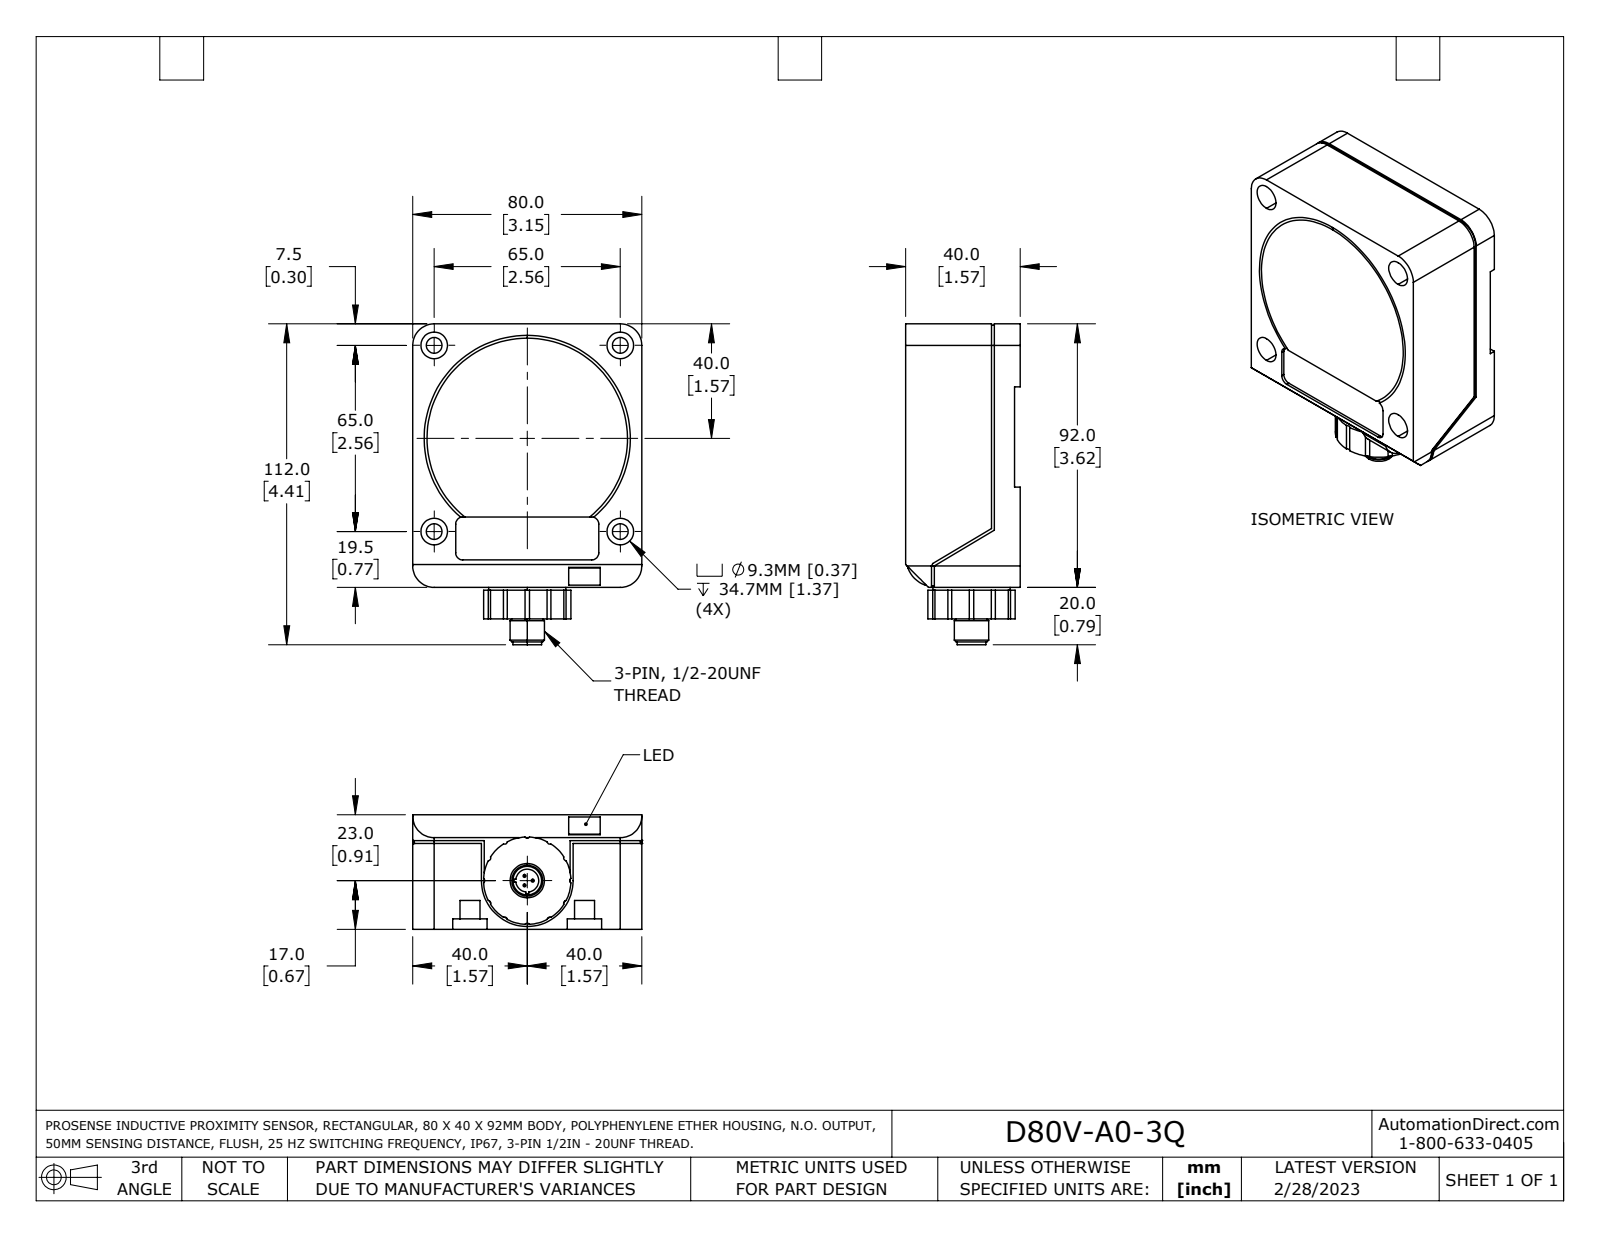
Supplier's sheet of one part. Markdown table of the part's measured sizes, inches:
| quantity | value |
| --- | --- |
| part name | D80V-A0-3M |
| STEP written by | SolidWorks 2021 (AUTOMOTIVE_DESIGN) |
| units | inches |
| bodies | 1 solid, 164 faces (85 planar, 70 cylindrical, 9 other) |
| overall size | 4.409 × 3.15 × 1.575 |
| volume | 17.35 in³ |
| surface area | 52.6 in² |
| round holes (diameter × count) | 0.217 × 4, 0.366 × 4, 0.315 × 1 |
| round bosses / shafts (diameter × count) | 0.04 × 3, 1.201 × 1, 1.063 × 1, 0.472 × 1, 0.394 × 1 |
| partial cylindrical surfaces (radius × count) | 0.039 × 12, 0.295 × 6, 0.098 × 4, 0.276 × 2, 0.394 × 1, 0.591 × 1, 0.63 × 1 |
| main face-to-face distances | 1.575, 0.079, 3.15, 1.496, 0.039, 3.622, 0.433, 1.535, 1.457, 4.055 |
| hole center spacings | 2.559, 3.619 |
